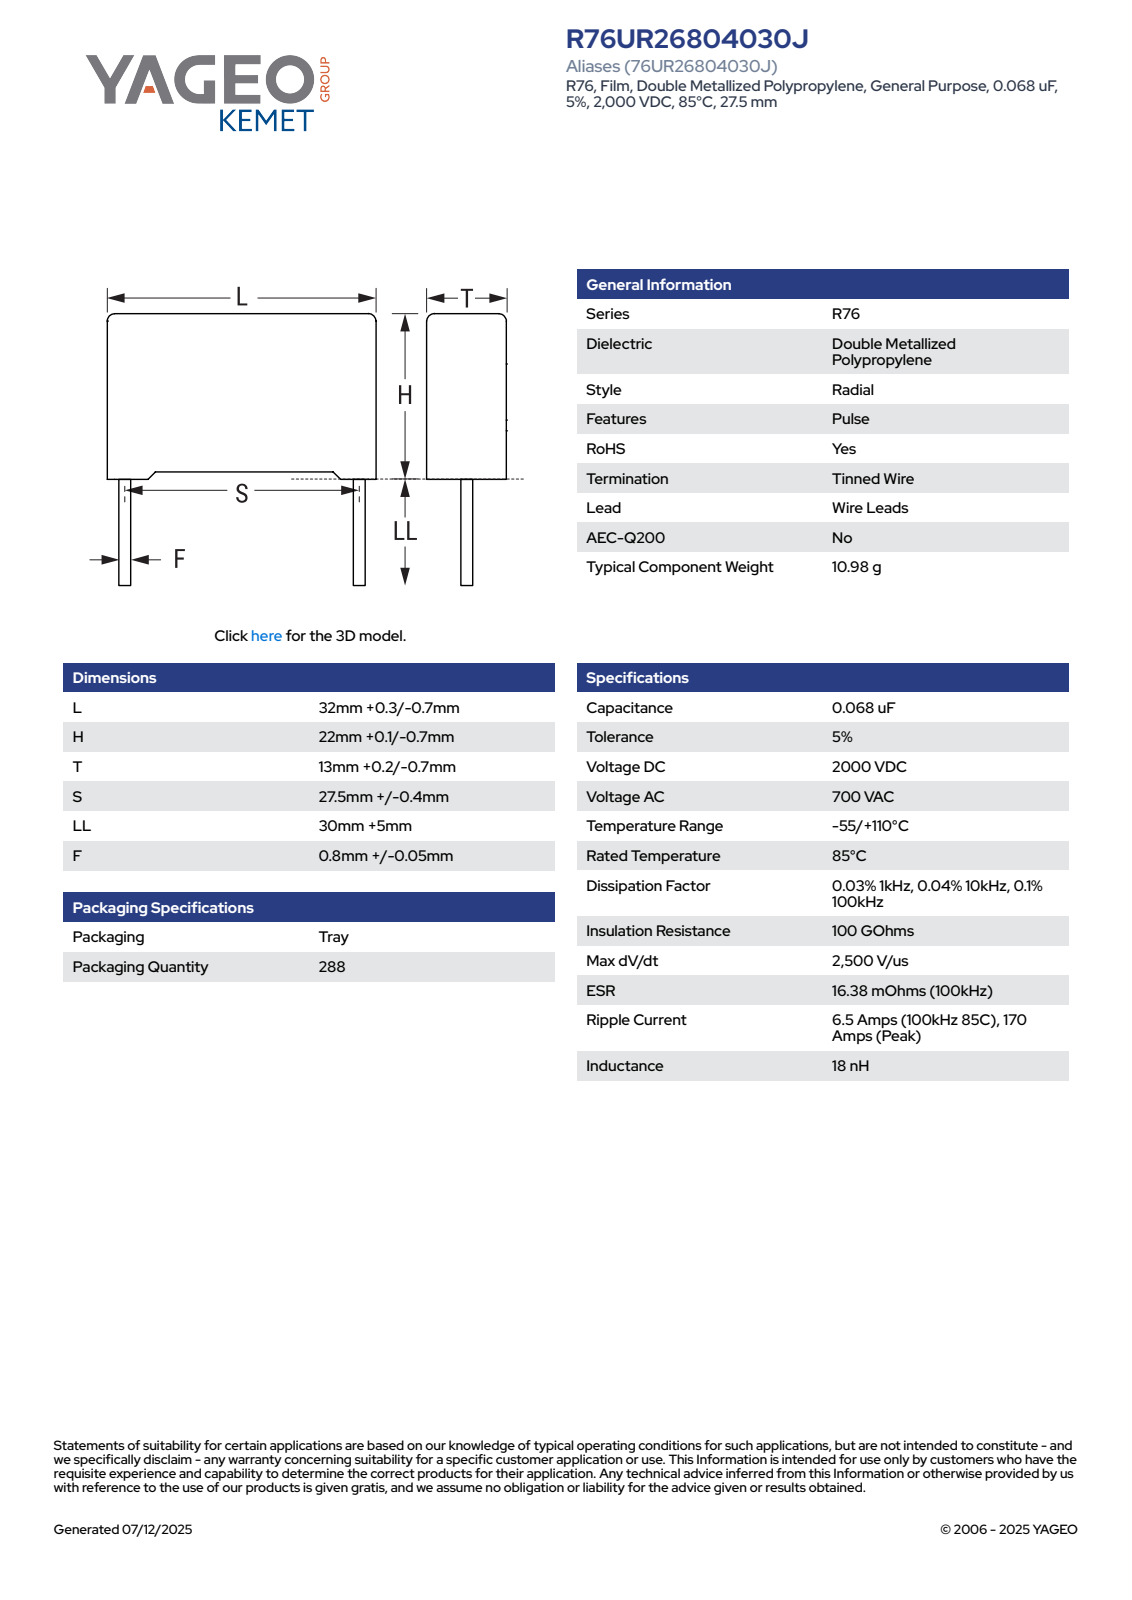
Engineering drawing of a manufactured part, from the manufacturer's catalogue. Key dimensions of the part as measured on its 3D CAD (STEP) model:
Part name (STEP PRODUCT): CFR_RB2_32X22X13_L32.3H22.1T13.2S27.5LL35F0.85
STEP written by: SolidWorks 2021 (AUTOMOTIVE_DESIGN)
Units: millimetres
Bodies: 4 solids, 85 faces (77 planar, 8 cylindrical, 0 other)
Overall size (bounding box): 57.1 × 32.3 × 13.21
Volume: 9 167 mm³ · Surface area: 3 105 mm²
Round bosses / shafts (diameter × count): ⌀0.85 ×2
Partial cylindrical surfaces — rounded edges, fillets, slot ends (radius × count): R0.5 ×4
Main face-to-face distances: 13.2, 21.34, 32.3, 21.35, 0.75, 0.76, 22.1, 1.08, 13.21, 31.22
